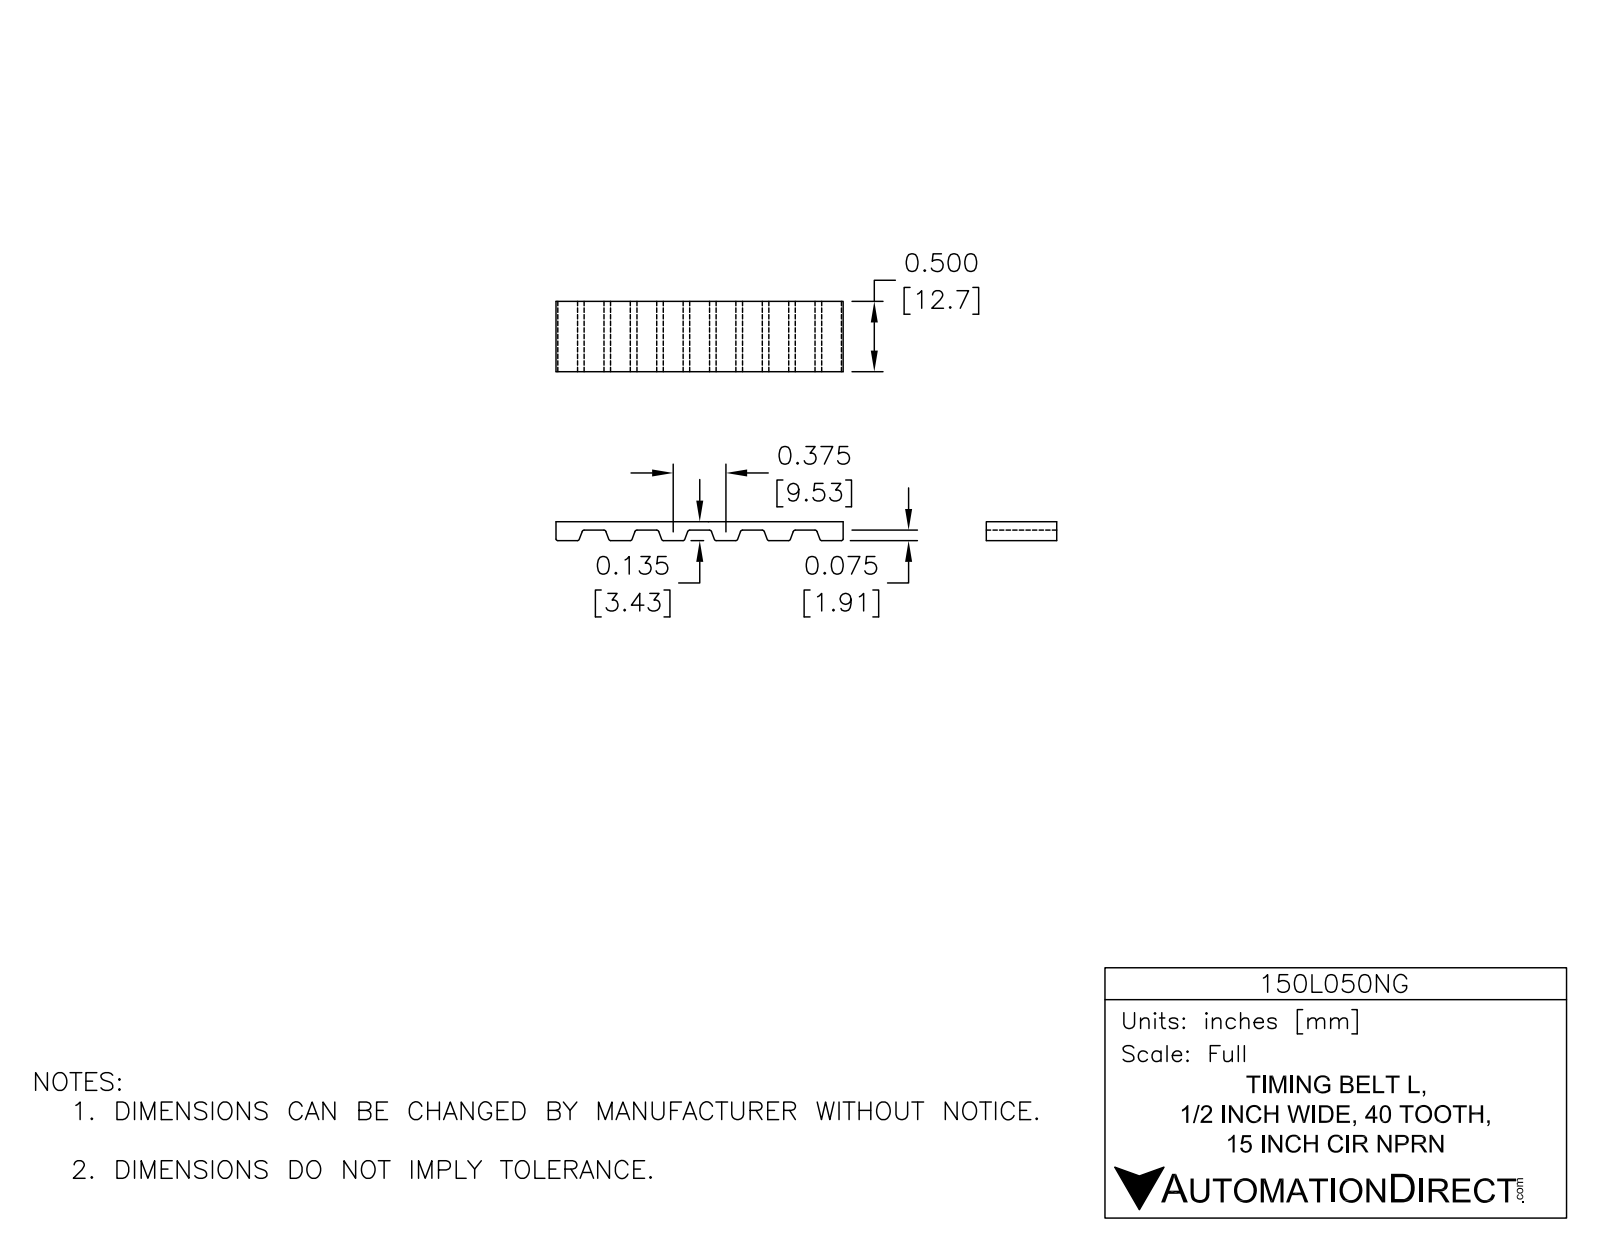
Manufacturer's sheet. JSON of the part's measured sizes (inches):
{"part_name": "150L050NG", "step_written_by": "SolidWorks 2014 (AUTOMOTIVE_DESIGN)", "units": "inches", "bodies": {"solids": 1, "faces": 334, "planar": 136, "cylindrical": 198, "other": 0}, "overall_size": [5.788, 3, 0.5], "volume_in3": 0.671, "surface_area_in2": 19.24, "partial_cylinders_radius": [[0.02, 156], [1.435, 2], [1.5, 2]], "face_to_face_distances": [0.065, 2.935, 3, 0.5, 2.87, 0.14, 2.86, 0.075, 2.795, 0.352]}
